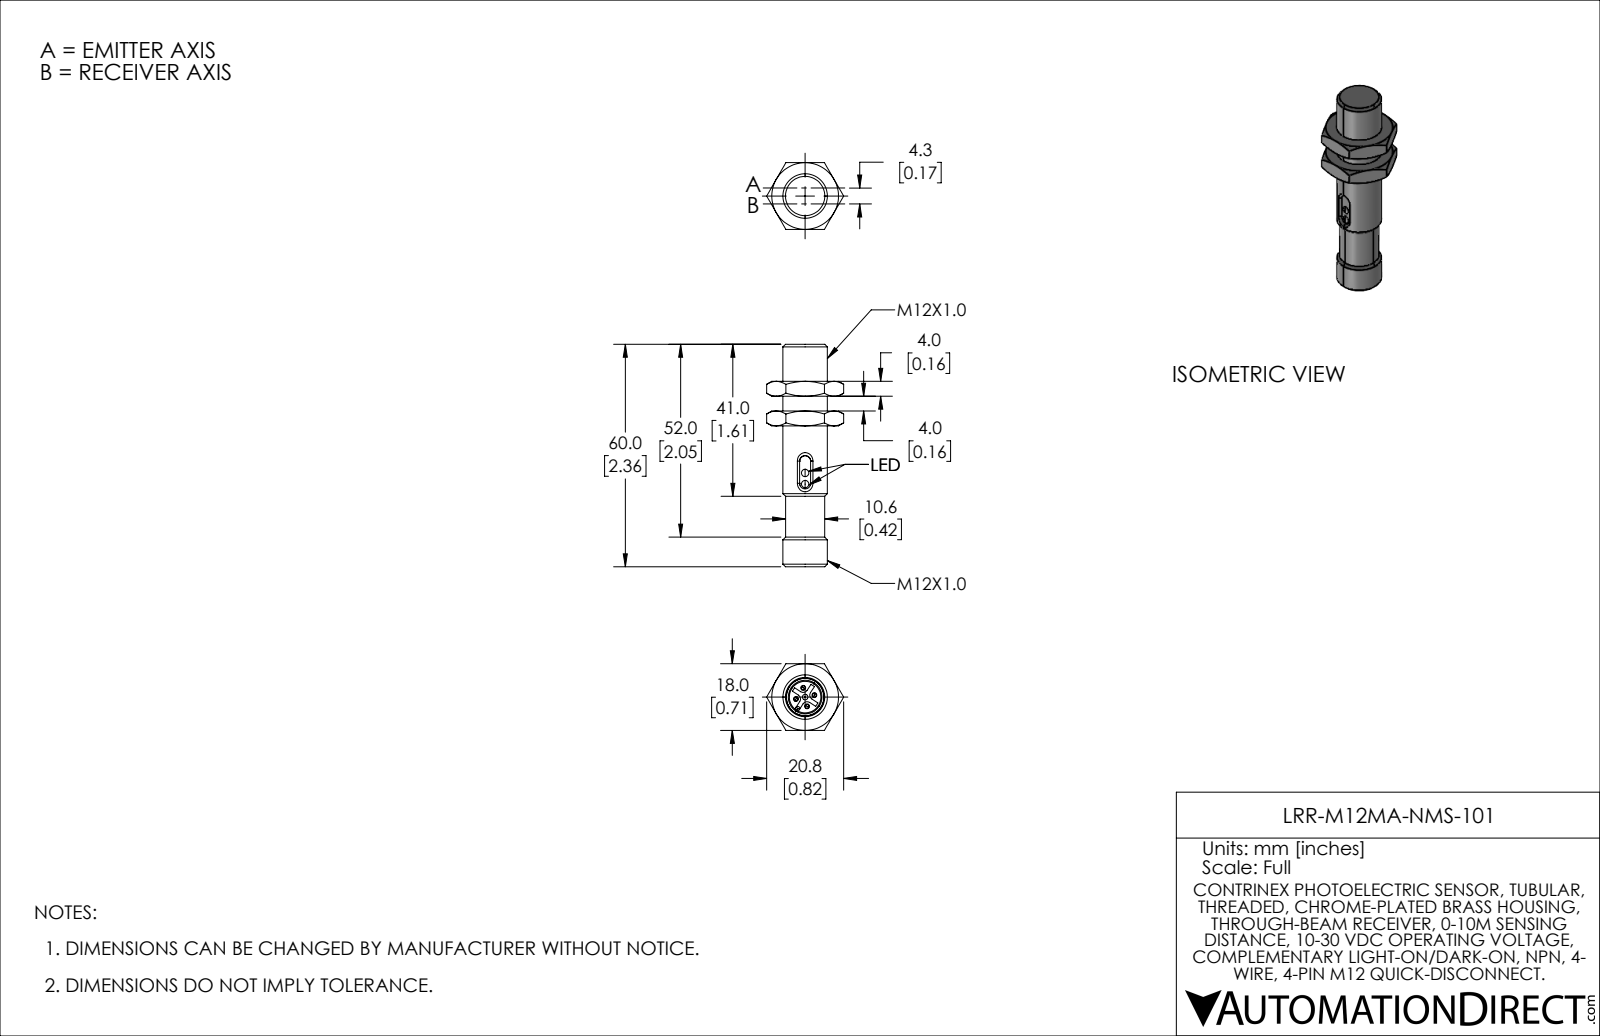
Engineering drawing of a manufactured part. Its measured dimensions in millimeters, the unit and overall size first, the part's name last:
Units: millimetres
Overall size (bounding box): 60 × 20.8 × 18
Round holes (diameter × count): ⌀1.5 ×1, ⌀8.5 ×1, ⌀10.2 ×1
Round bosses / shafts (diameter × count): ⌀1 ×4, ⌀12 ×1, ⌀10.5 ×1
Partial cylindrical surfaces — rounded edges, fillets, slot ends (radius × count): R1.2 ×4, R0.5 ×2, R1.5 ×2, R0.6 ×1
Main face-to-face distances: 10, 18, 6, 16, 4, 20, 26, 51.2, 41.2, 35.2
Volume: 8 290 mm³ · Surface area: 4 582 mm²
Bodies: 3 solids, 161 faces (44 planar, 50 cylindrical, 67 other)
Part name (STEP PRODUCT): LRR-M12MA-NMS-101
STEP written by: SolidWorks 2021 (AUTOMOTIVE_DESIGN)
